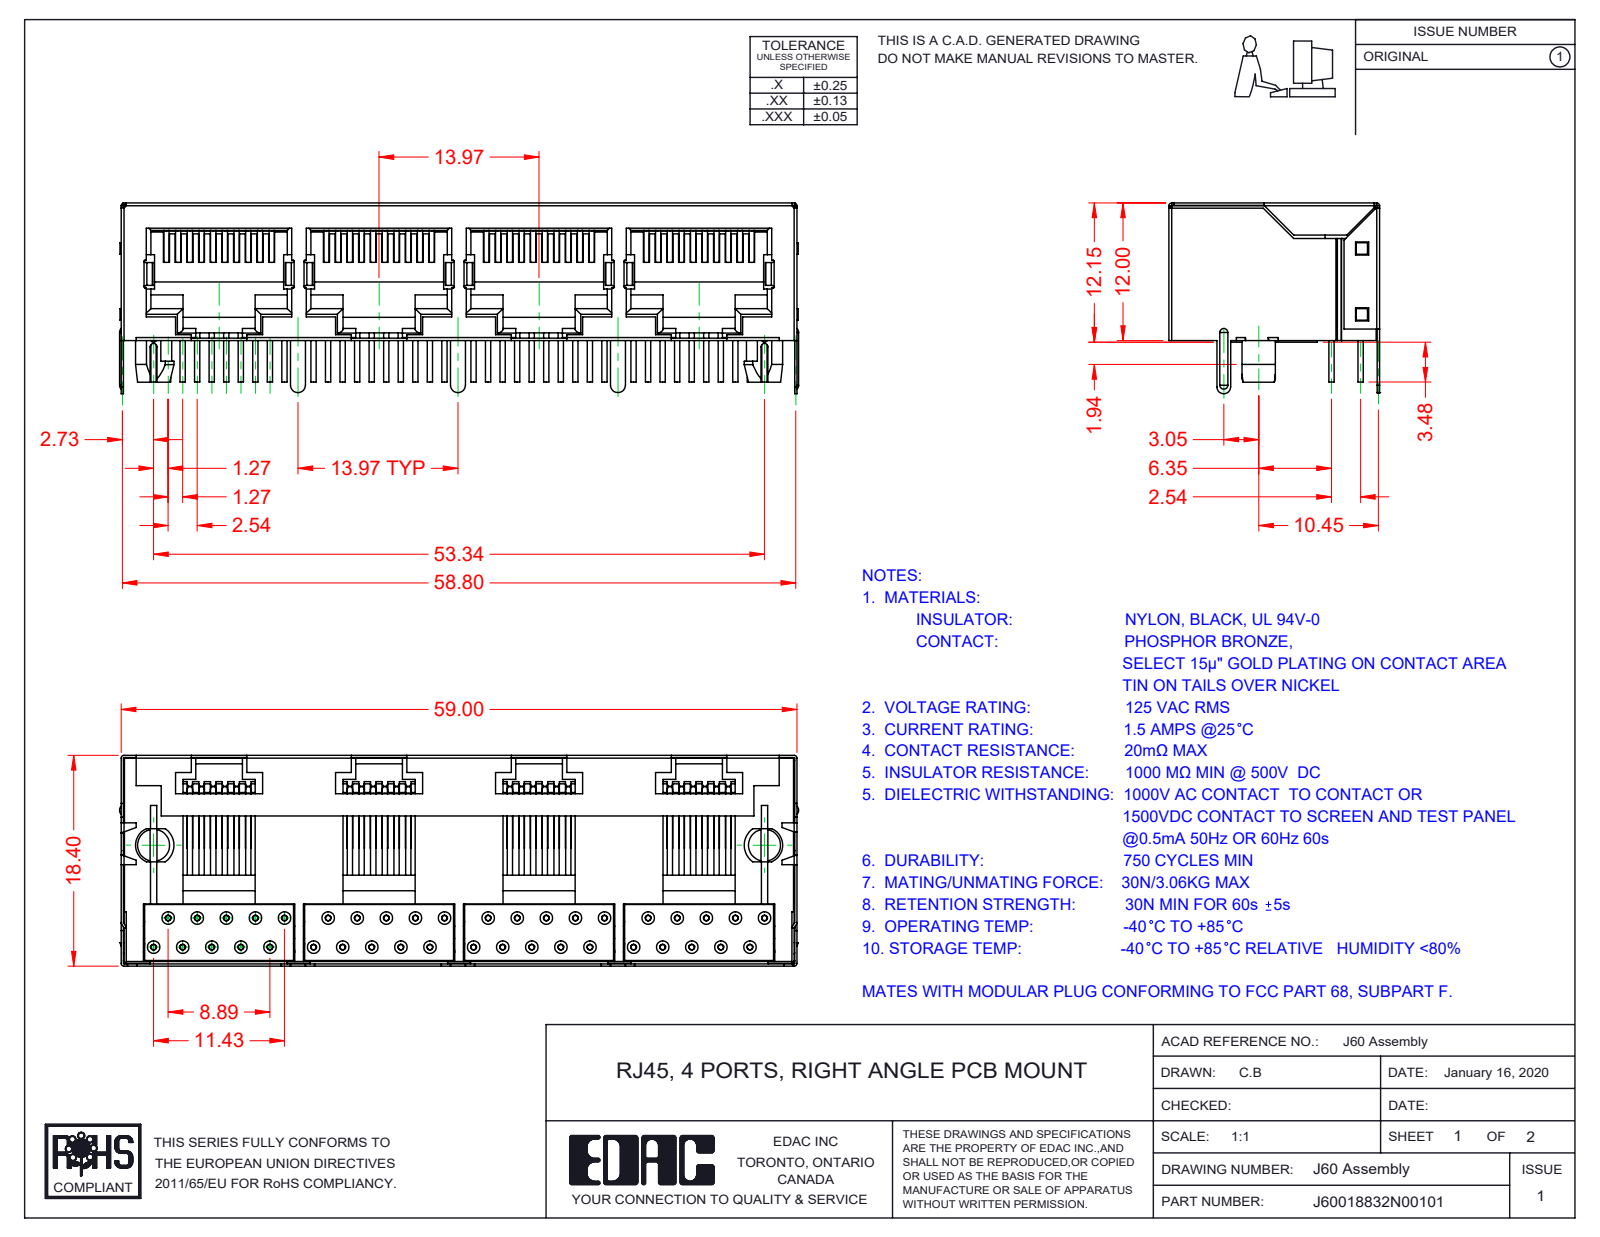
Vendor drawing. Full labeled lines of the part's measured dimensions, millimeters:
Part name (STEP PRODUCT): 60 Shield; 60 Insulator; RJ60041132N00101; 60 Contacts_10P10C
STEP written by: SolidWorks 2016 (CONFIG_CONTROL_DESIGN)
Units: millimetres
Bodies: 42 solids, 2674 faces (1505 planar, 763 cylindrical, 406 other)
Overall size (bounding box): 59.3 × 18.4 × 16.65
Volume: 7 062 mm³ · Surface area: 18 987 mm²
Round holes (diameter × count): ⌀0.5 ×40, ⌀1.1 ×40
Round bosses / shafts (diameter × count): ⌀0.46 ×120
Partial cylindrical surfaces — rounded edges, fillets, slot ends (radius × count): R0.3 ×26, R0.25 ×21, R0.5 ×18, R0.1 ×16, R0.21 ×10, R0.8 ×7, R0.65 ×3, R0.28 ×2
Main face-to-face distances: 0.5, 11.75, 11.55, 13.97, 2.19, 5.38, 5.18, 4.88, 18.2, 11.5
Hole centre spacings: 2.84, 2.54, 4.58, 13.97, 5.08, 12.95, 15.45, 11.43
